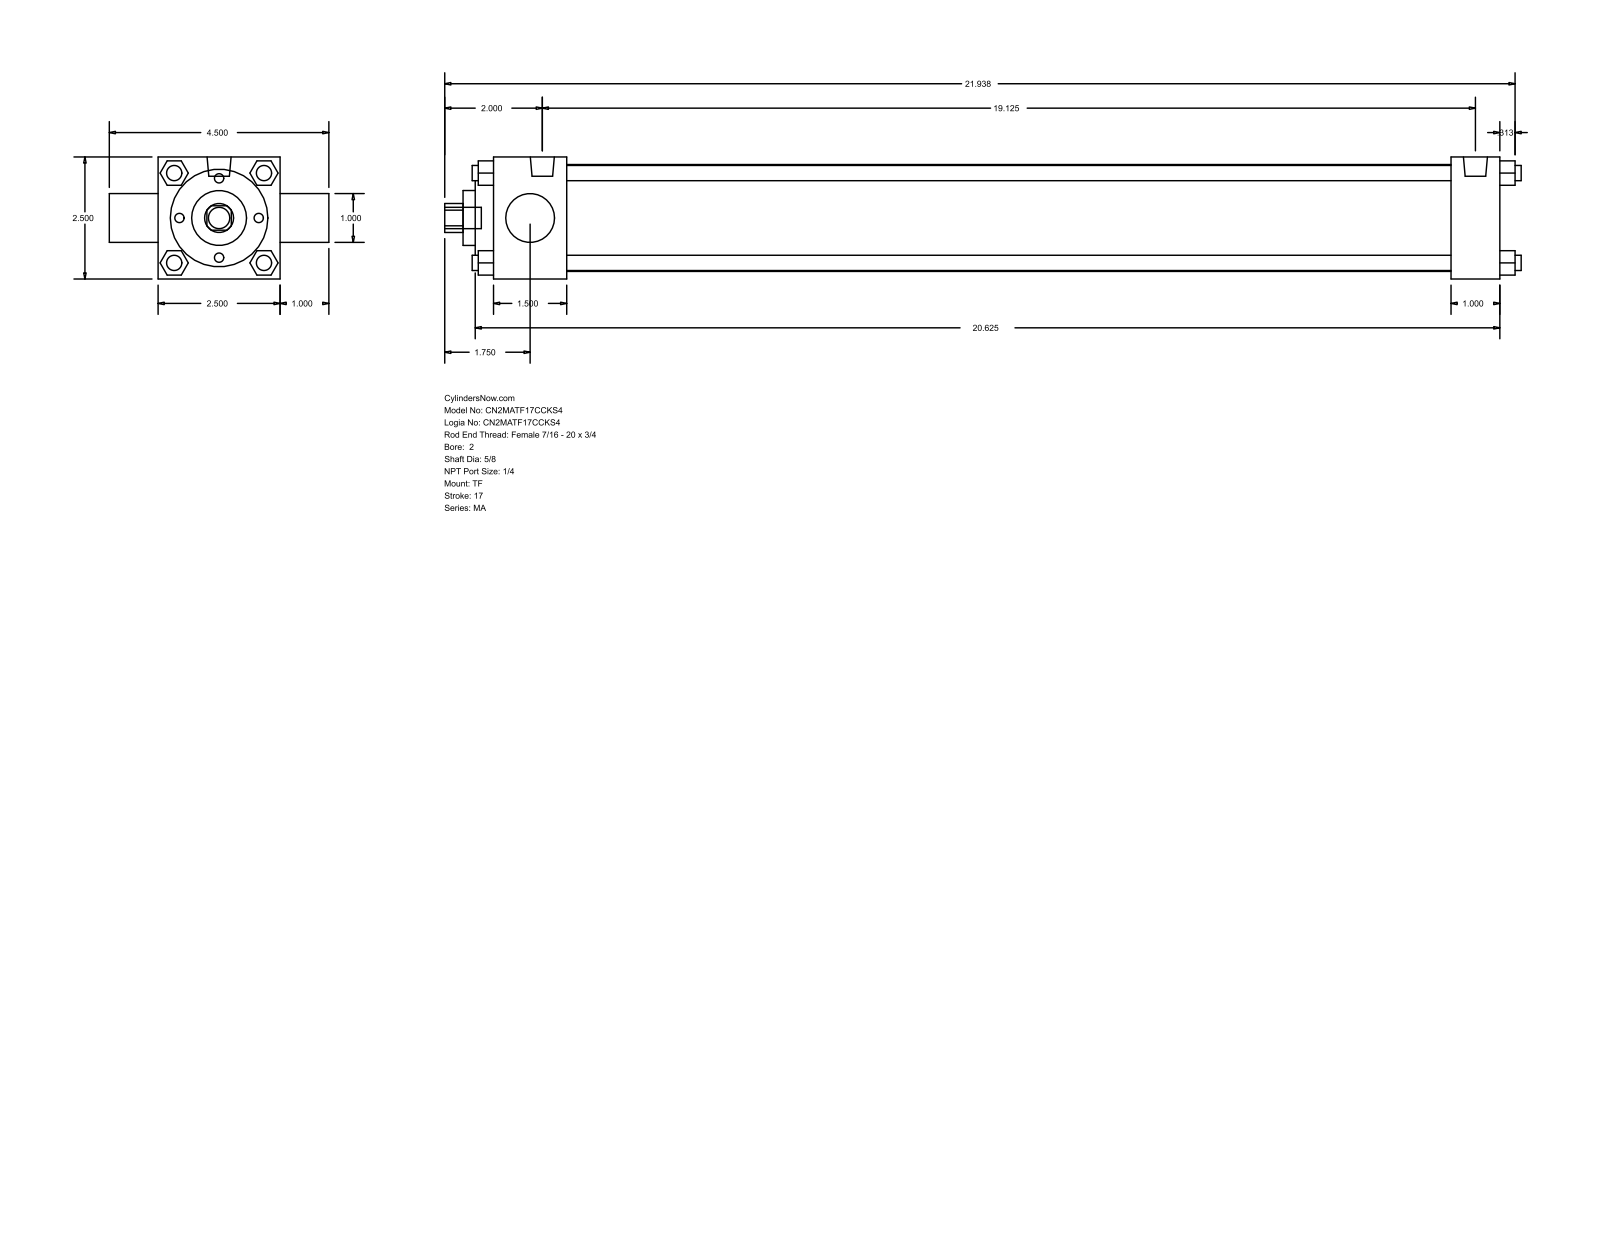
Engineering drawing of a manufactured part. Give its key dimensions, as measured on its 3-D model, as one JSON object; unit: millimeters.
{"part_name": "MA_TF__0200_0.625", "step_written_by": "GSSL Pune (CONFIG_CONTROL_DESIGN)", "units": "millimeters", "bodies": {"solids": 0, "faces": 122, "planar": 93, "cylindrical": 29, "other": 0}, "overall_size": [560.39, 114.3, 63.5], "round_holes": [[15.88, 1], [25.4, 1], [28.57, 1], [50.8, 1], [55.63, 1]], "round_bosses_or_shafts": [[7.94, 7], [12.49, 2], [11.11, 1]], "partial_cylinders_radius": [[7.54, 1]], "face_to_face_distances": [63.5, 38.1, 12.7, 9.52, 523.87, 498.48, 460.38, 485.77, 25.39, 47.62]}
